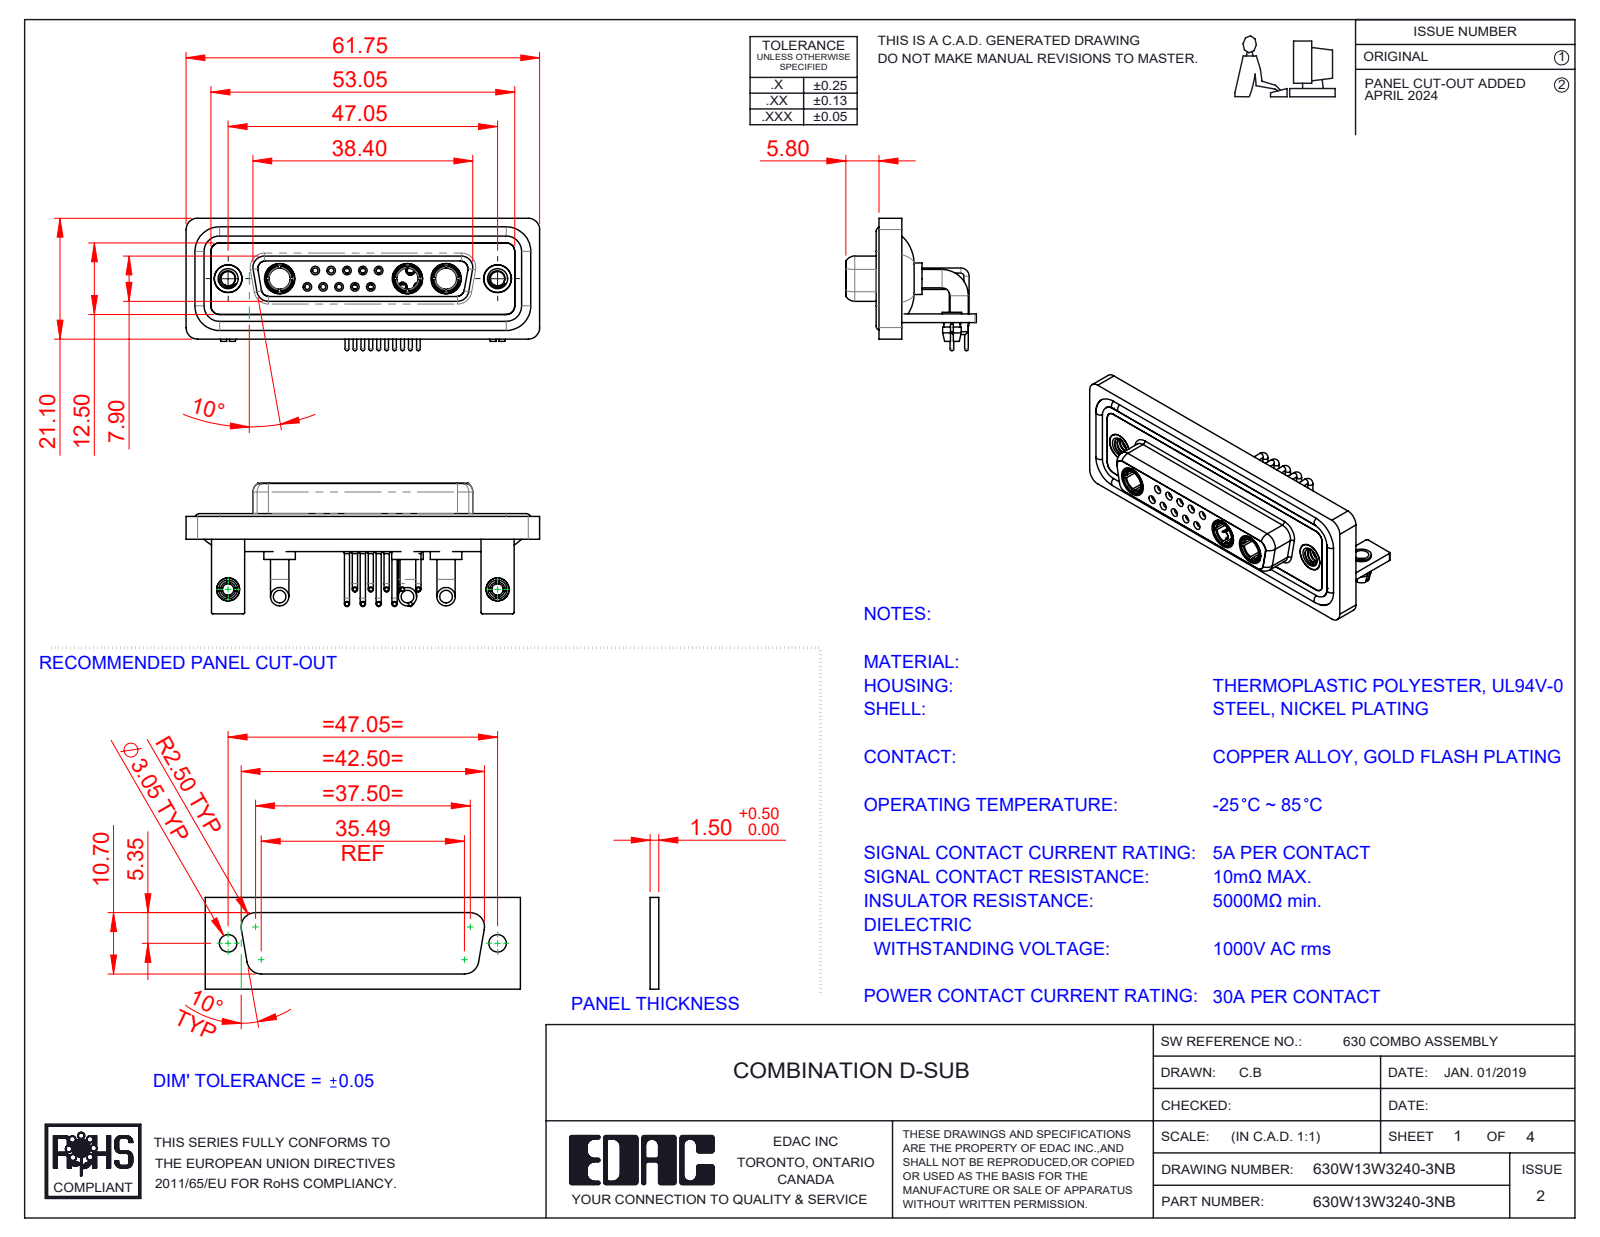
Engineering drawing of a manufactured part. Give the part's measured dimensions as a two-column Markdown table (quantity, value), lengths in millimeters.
| quantity | value |
| --- | --- |
| part name | 630Combo Stabilizer Bracket_50 Contacts; 630W13W3240-3NB; 630Combo Waterproof Housing_25 Contacts; Power Socket_30A RA (+7 more) |
| STEP written by | SolidWorks 2023 (CONFIG_CONTROL_DESIGN) |
| units | millimeters |
| bodies | 27 solids, 1284 faces (410 planar, 547 cylindrical, 327 other) |
| overall size | 61.75 × 23.12 × 22.8 |
| volume | 8 950 mm³ |
| surface area | 15 301 mm² |
| round holes (diameter × count) | 2 × 12, 0.9 × 10, 1.1 × 10, 1.5 × 10, 1.6 × 5, 1.7 × 5, 4.85 × 5, 2.5 × 4, 3.7 × 3, 5.3 × 3, 3.2 × 2, 4 × 2 |
| round bosses / shafts (diameter × count) | 0.9 × 15, 1.6 × 12, 0.65 × 10, 3.2 × 6, 2 × 5, 1.5 × 5, 5.5 × 3, 5.2 × 3 |
| partial cylindrical surfaces (radius × count) | 2 × 19, 1.5 × 18, 0.25 × 16, 1.35 × 8, 1.6 × 8, 0.5 × 5, 0.6 × 4, 0.65 × 4 |
| main face-to-face distances | 0.4, 1.8, 2.9, 3.7, 1.5, 4.1, 1.1, 1.4, 1.6, 3.1 |
| hole center spacings | 3.16, 2.77, 5.54, 5.04, 8.31, 5.03, 7.49, 11.08 |
